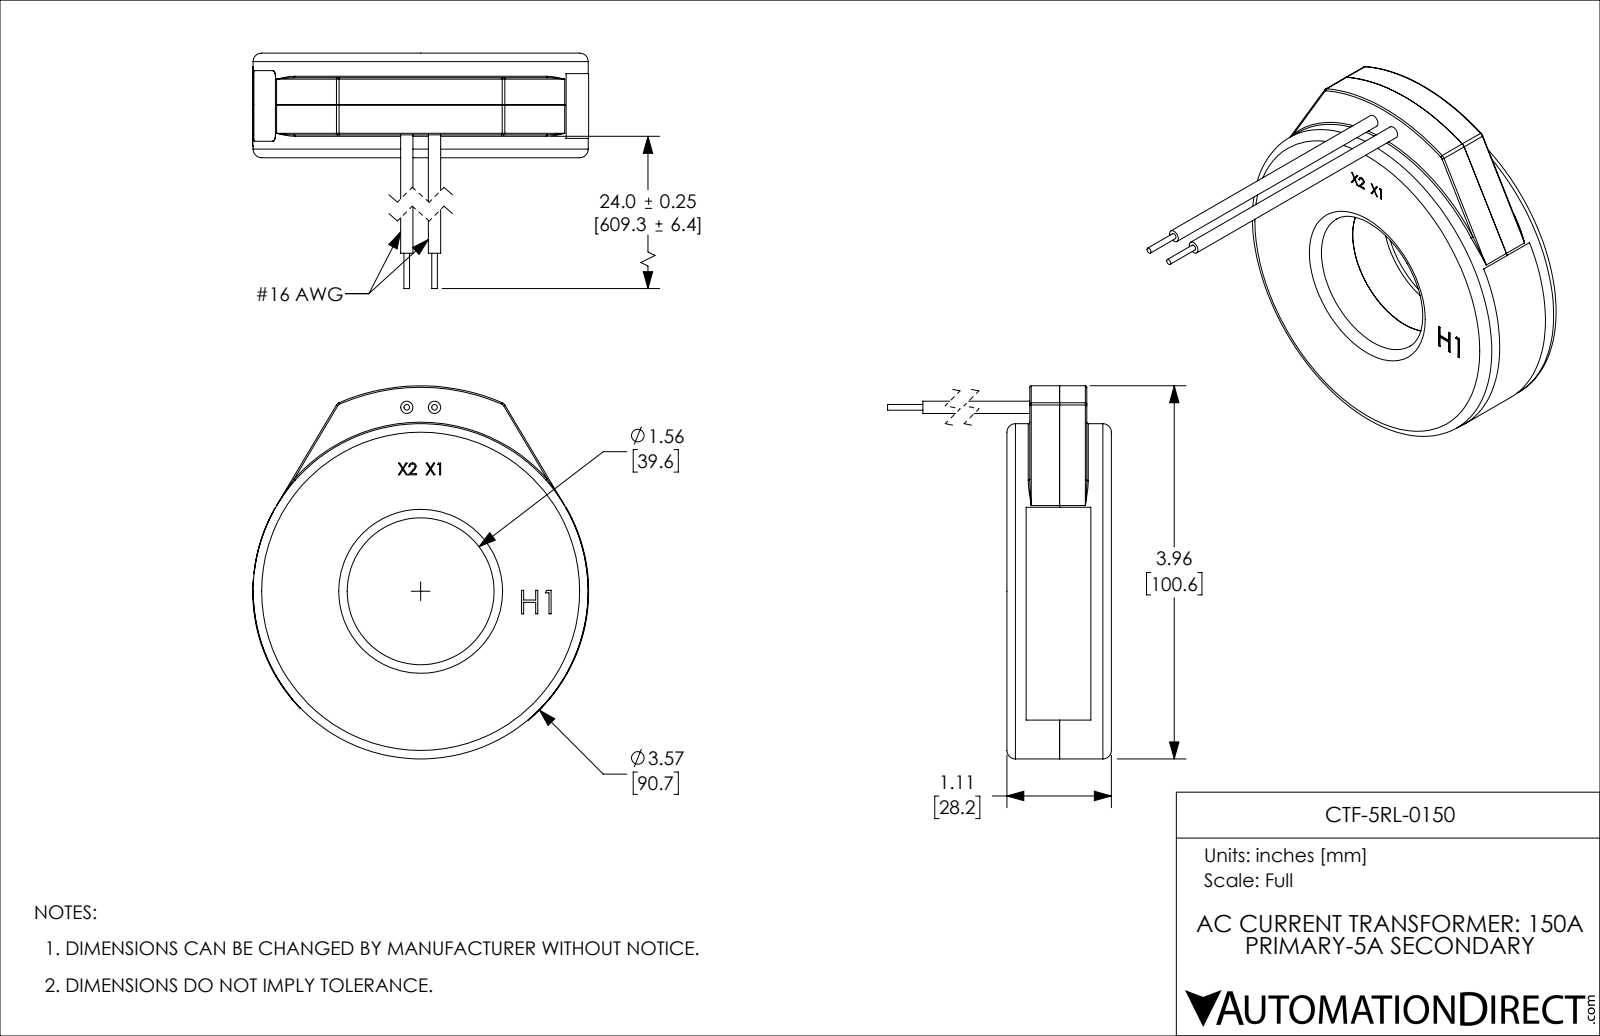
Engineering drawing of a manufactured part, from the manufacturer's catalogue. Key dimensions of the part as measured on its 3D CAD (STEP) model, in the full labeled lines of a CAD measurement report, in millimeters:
Part name (STEP PRODUCT): CTF-5RL-0150
STEP written by: SolidWorks 2018 (AUTOMOTIVE_DESIGN)
Units: millimetres
Bodies: 7 solids, 154 faces (87 planar, 37 cylindrical, 30 other)
Overall size (bounding box): 107.7 × 100.6 × 90.7
Volume: 156 500 mm³ · Surface area: 40 440 mm²
Round holes (diameter × count): ⌀39.6 ×1
Round bosses / shafts (diameter × count): ⌀3.3 ×2, ⌀1.5 ×2, ⌀90.4 ×1
Partial cylindrical surfaces — rounded edges, fillets, slot ends (radius × count): R3.2 ×3, R0.4 ×2, R0.4 ×2, R1.5 ×2, R45.2 ×1, R45.3 ×1, R45.3 ×1, R55.4 ×1
Main face-to-face distances: 14, 28.2, 14.2, 22, 8.1, 6.2, 6.6, 7.3, 15.4, 21.6
